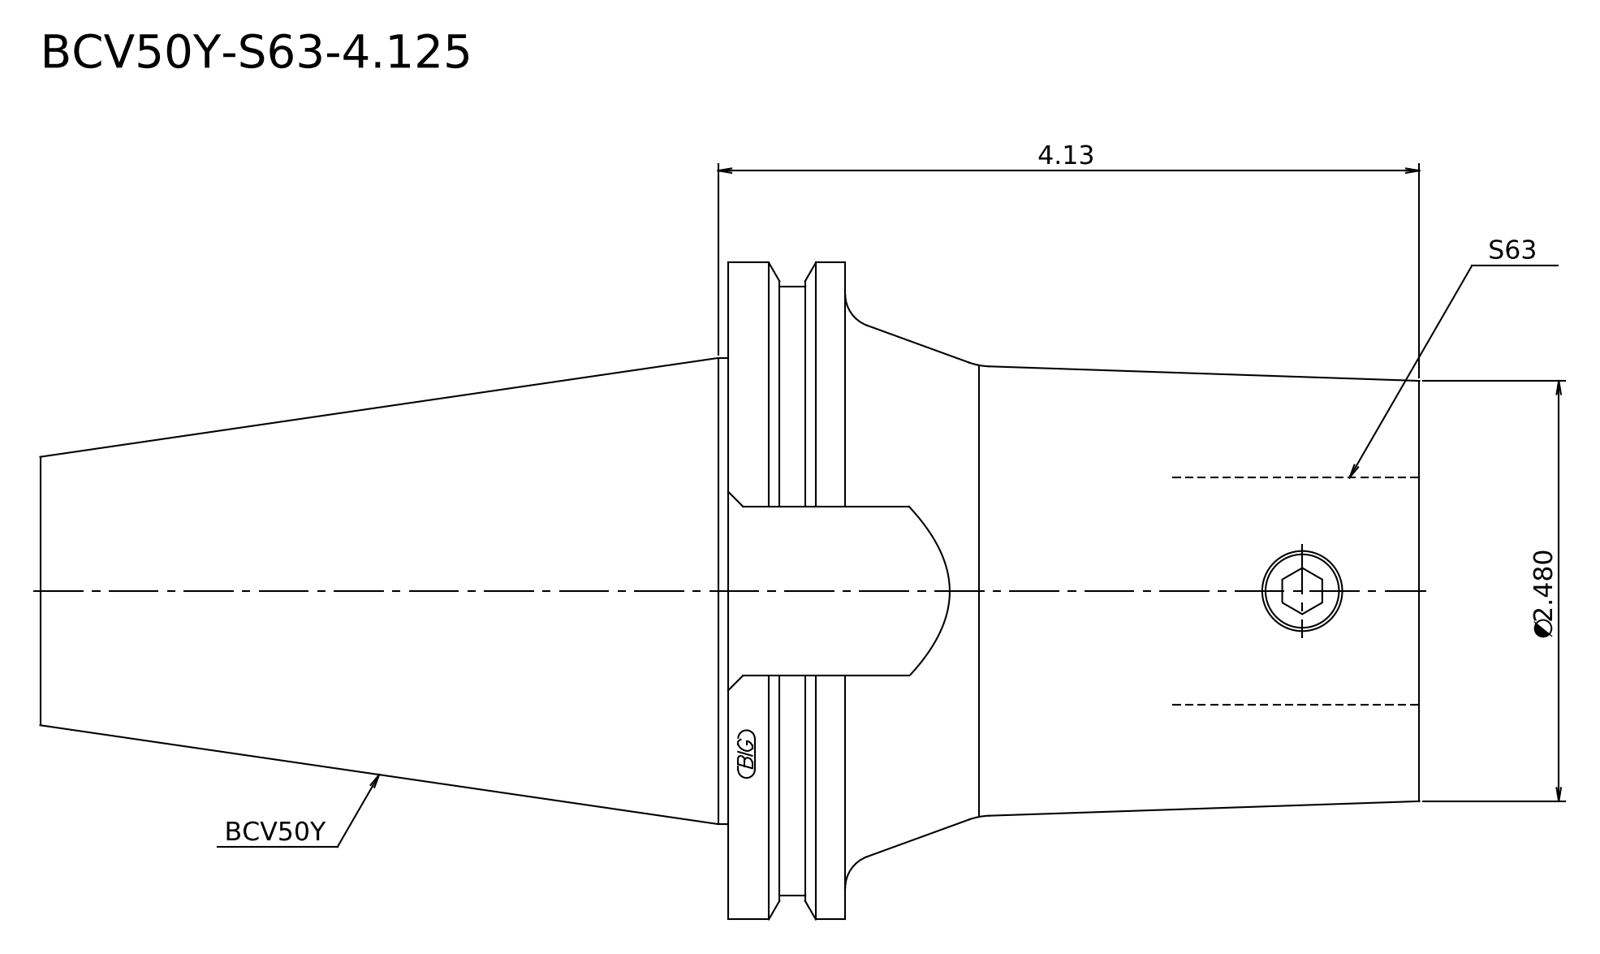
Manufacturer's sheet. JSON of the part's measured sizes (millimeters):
{"step_written_by": "Kubotek KeyCreator 2011 V10.0.2 (22737) (automotive_design)", "units": "millimeters", "bodies": {"solids": 1, "faces": 16, "planar": 6, "cylindrical": 4, "other": 6}, "overall_size": [206.7, 98.42, 98.42], "volume_mm3": 692580, "surface_area_mm2": 53543, "round_bosses_or_shafts": [[98.42, 1], [91.29, 1], [69.85, 1]], "face_to_face_distances": [103.6, 86.05, 17.55, 206.7, 120.65, 103.1, 95.9, 9.85, 7.7, 110.8]}
